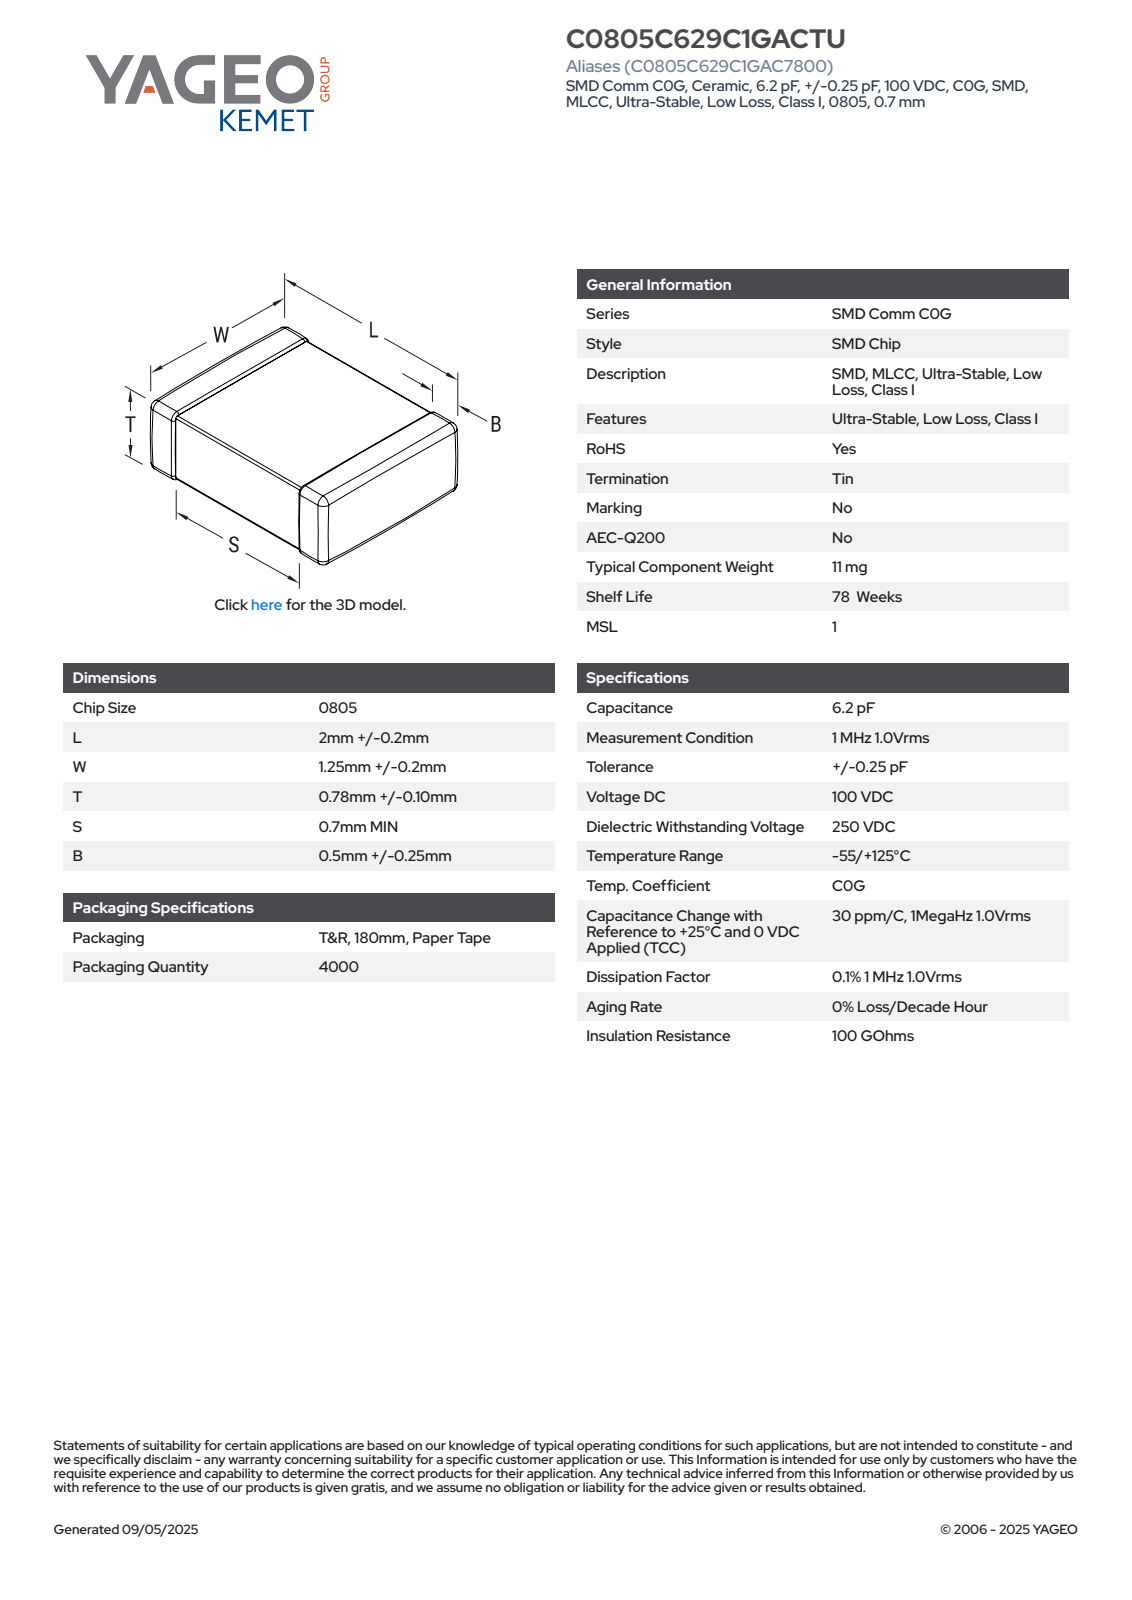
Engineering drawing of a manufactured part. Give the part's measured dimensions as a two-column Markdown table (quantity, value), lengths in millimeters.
| quantity | value |
| --- | --- |
| part name | CCS_CCSTD_0805_L2.2W1.45T0.88B0.5 |
| STEP written by | SolidWorks 2021 (AUTOMOTIVE_DESIGN) |
| units | millimeters |
| bodies | 4 solids, 125 faces (71 planar, 38 cylindrical, 16 other) |
| overall size | 2.2 × 1.45 × 0.88 |
| volume | 3 mm³ |
| surface area | 13 mm² |
| main face-to-face distances | 0.85, 0.82, 1.42, 0.88, 2.2, 1.39, 1.45, 0.97, 1.23, 1.19 |
